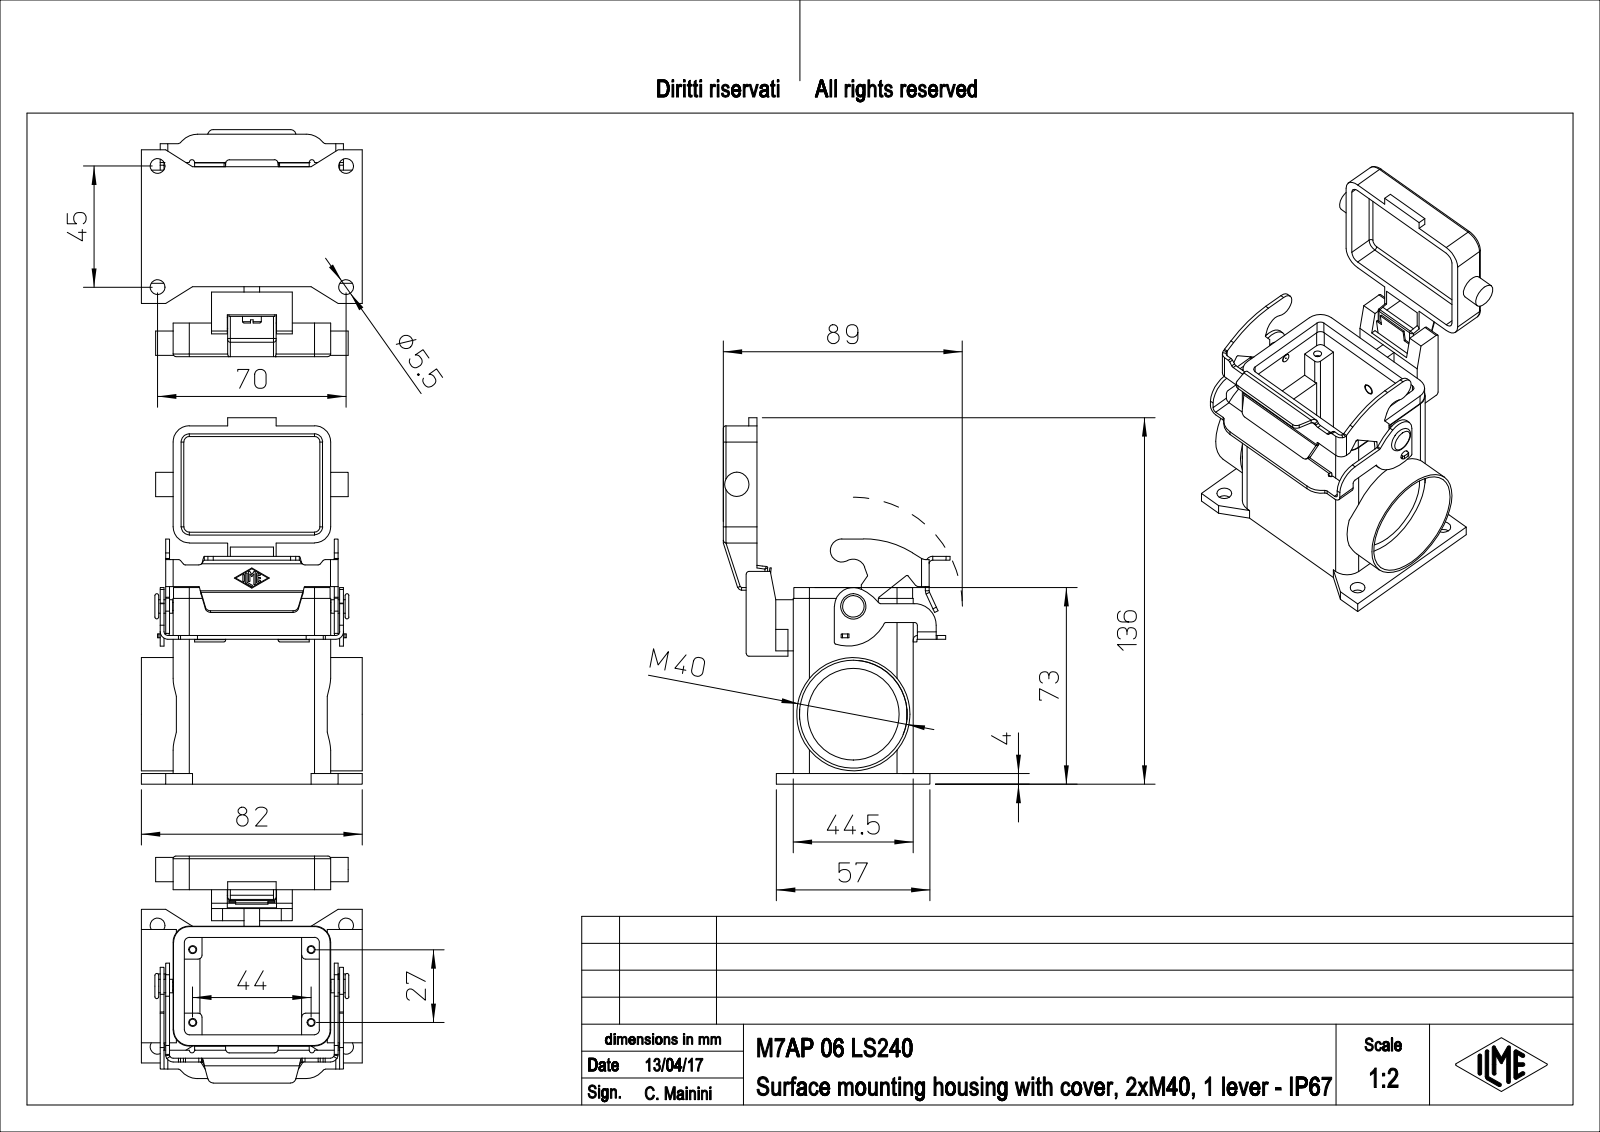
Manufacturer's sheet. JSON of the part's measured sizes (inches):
{"part_name": "M7AP_06_LS240", "step_written_by": "PTC Creo Elements/Direct Modeling 19.0E 27-Jun-2016 (C) Parametric Technology GmbH (AUTOMOTIVE_DESIGN)", "units": "inches", "bodies": {"solids": 1, "faces": 550, "planar": 285, "cylindrical": 225, "other": 40}, "overall_size": [5.354, 3.316, 3.228], "volume_in3": 6.166, "surface_area_in2": 98.68, "round_holes": [[0.097, 4], [0.118, 4], [0.217, 4], [0.138, 1], [0.157, 1], [1.339, 1], [1.575, 1]], "round_bosses_or_shafts": [[1.654, 1], [0.354, 1], [0.276, 1], [0.197, 1], [0.157, 1], [0.126, 1], [0.118, 1]], "partial_cylinders_radius": [[0.039, 31], [0.01, 16], [0.02, 13], [0.059, 12], [0.079, 8], [0.236, 8], [0.055, 6], [0.11, 6]], "face_to_face_distances": [0.157, 1.594, 0.055, 1.752, 1.024, 1.181, 1.437, 2.52, 2.677, 2.776], "hole_center_spacings": [0.622, 1.507, 2.272, 2.654, 1.063, 1.732, 1.772, 2.032]}
